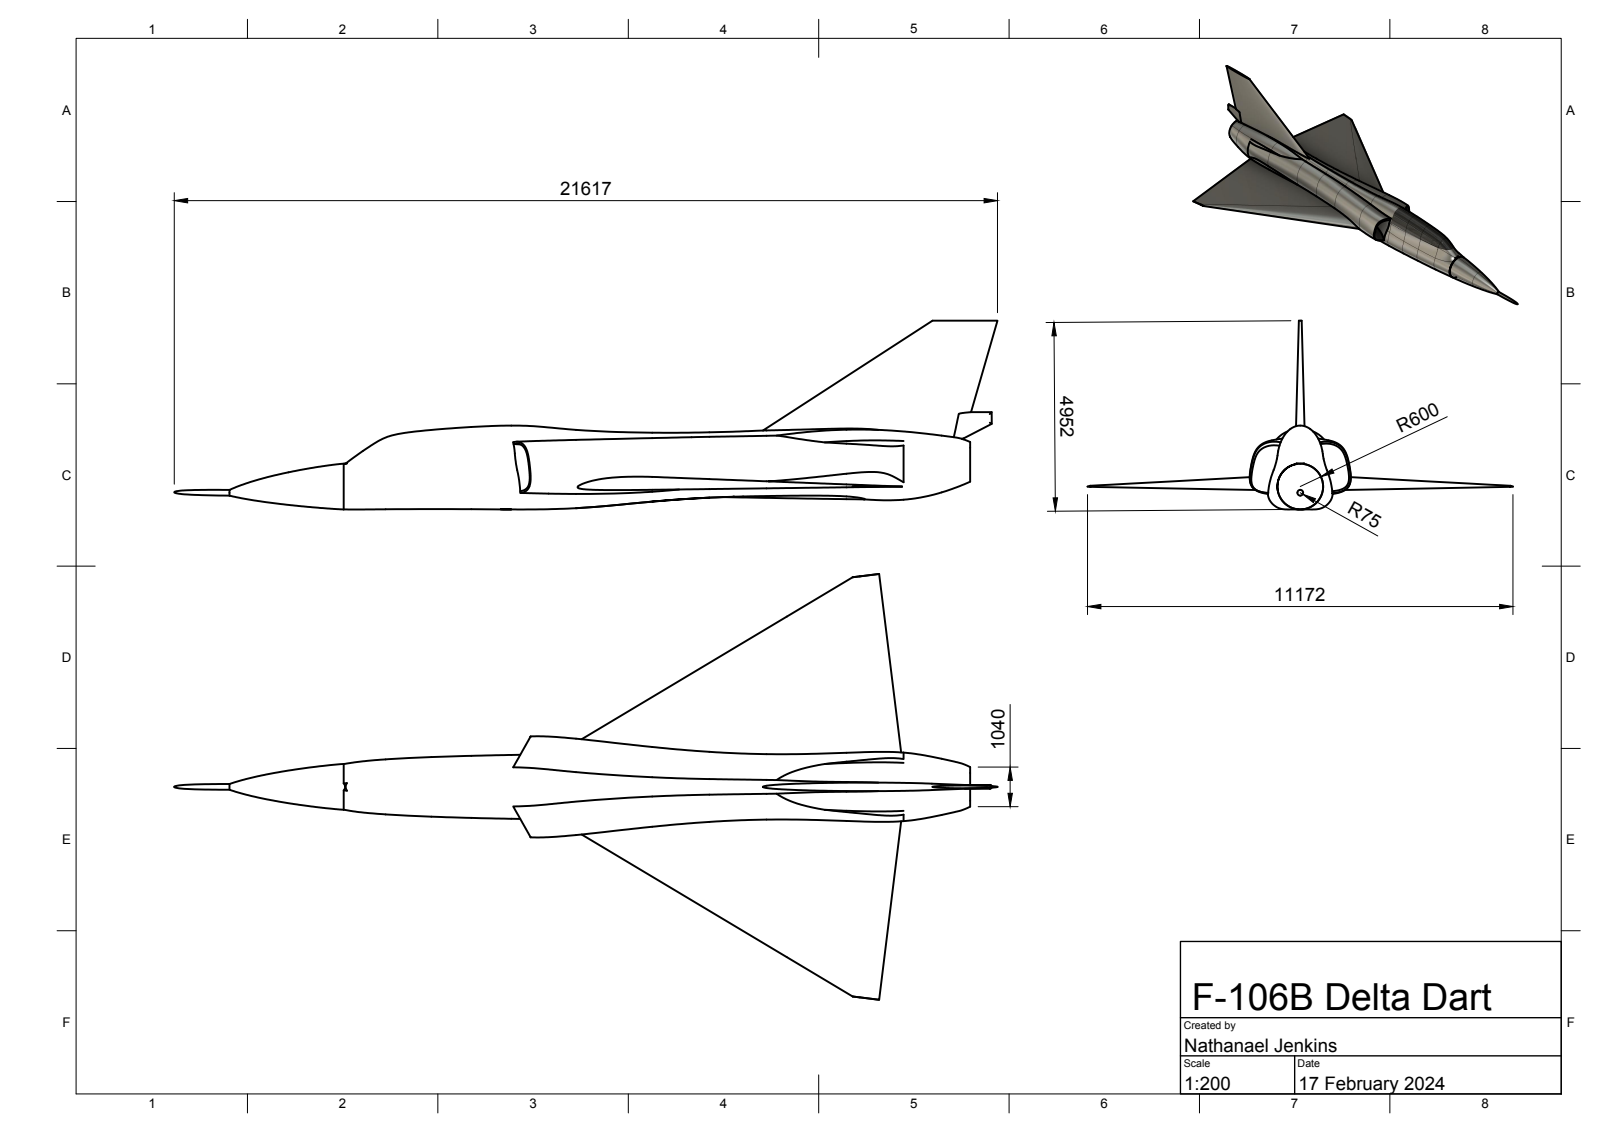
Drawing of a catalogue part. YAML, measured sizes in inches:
part_name: "F-106B v4"
step_written_by: "Autodesk Translation Framework v12.14.0.127 (AUTOMOTIVE_DESIGN)"
units: inches
bodies: {solids: 1, faces: 146, planar: 10, cylindrical: 7, other: 129}
overall_size: [851.054, 439.839, 195.032]
volume: 2457000
surface_area: 406300
partial_cylinders:
  - {radius: 1.969, count: 3}
  - {radius: 23.611, count: 1}
face_to_face_distances: [3.937]
